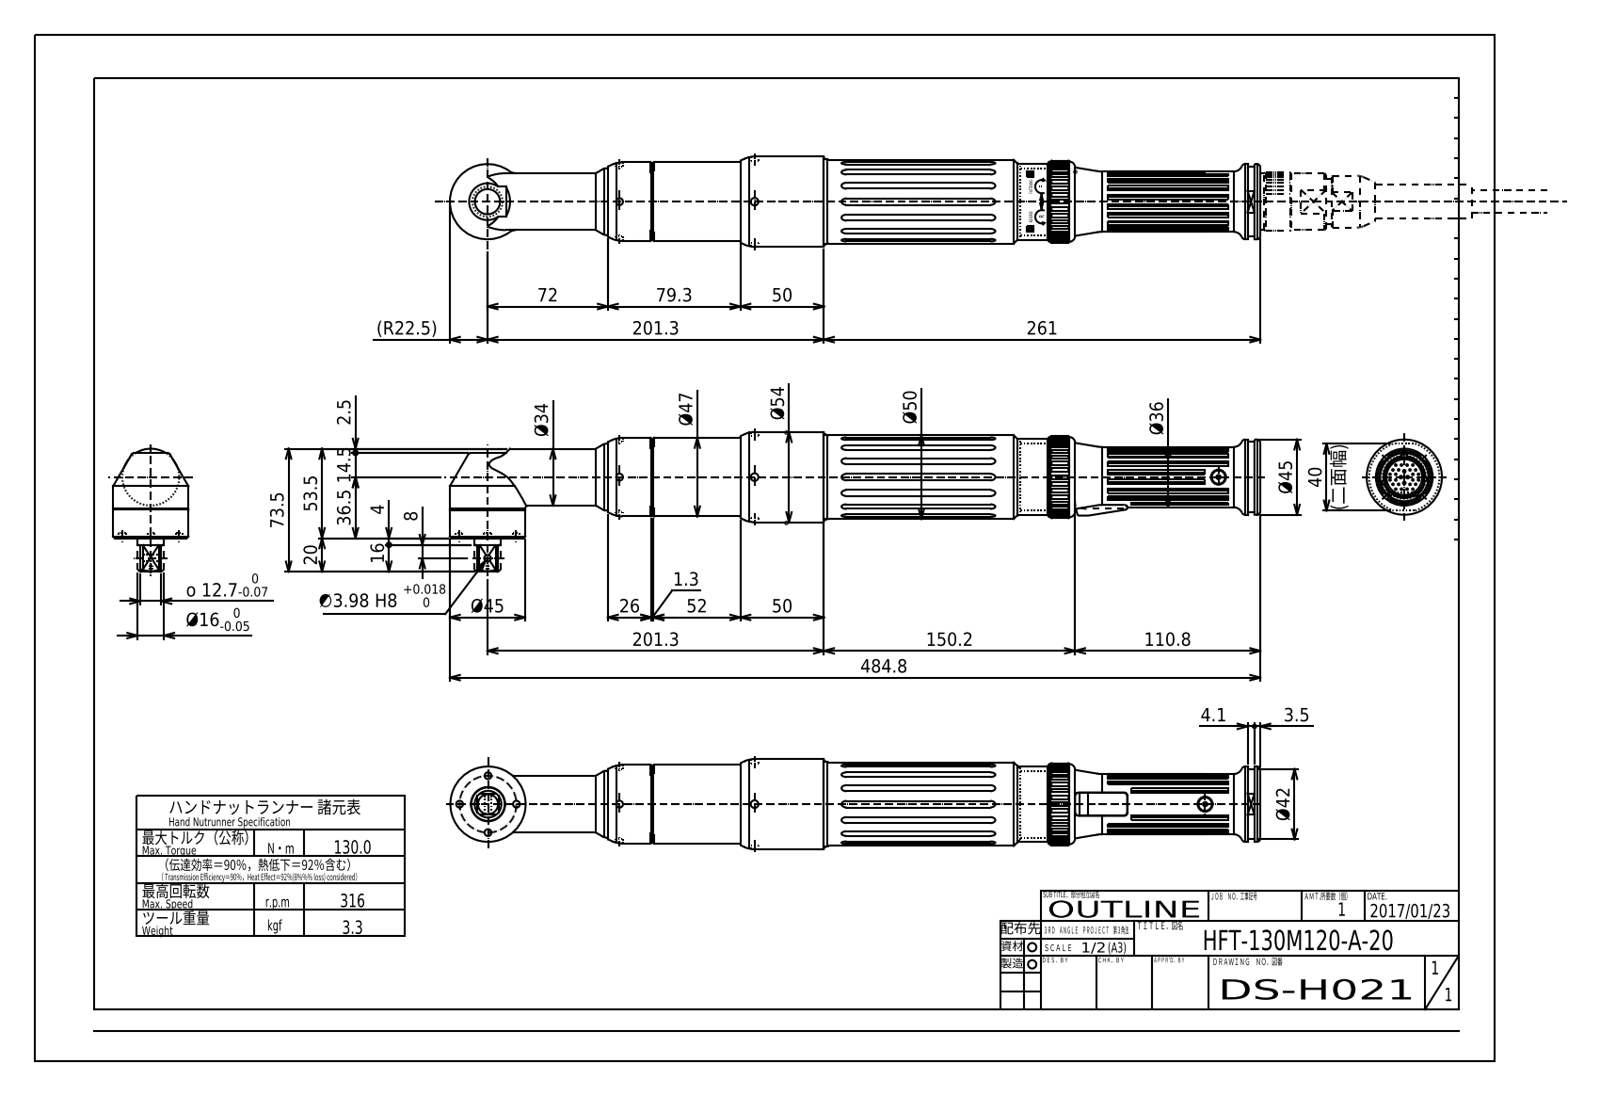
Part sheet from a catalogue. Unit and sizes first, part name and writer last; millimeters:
Units: millimetres
Overall size (bounding box): 484.75 × 83.5 × 54
Round holes (diameter × count): ⌀4.1 ×4, ⌀4.6 ×4, ⌀9 ×2, ⌀1.6 ×1, ⌀3 ×1, ⌀3.98 ×1, ⌀4.5 ×1, ⌀6 ×1, ⌀6.8 ×1, ⌀15 ×1, ⌀20.5 ×1, ⌀22.6 ×1
Round bosses / shafts (diameter × count): ⌀1 ×24, ⌀1.6 ×4, ⌀45 ×2, ⌀8 ×2, ⌀54 ×1, ⌀52 ×1, ⌀50 ×1, ⌀48 ×1
Partial cylindrical surfaces — rounded edges, fillets, slot ends (radius × count): R0.1 ×36, R1.5 ×36, R0.33 ×18, R3 ×18, R0.3 ×6, R1 ×6, R2.5 ×6, R0.88 ×2
Main face-to-face distances: 34.96, 1, 0.5, 15.6, 12.1, 3.5, 1.5, 3, 12.7, 11.13
Hole centre spacings: 17, 24.04, 34, 80.75, 80.81, 160.65, 360.05, 371.04
Volume: 763 308 mm³ · Surface area: 89 402 mm²
Bodies: 1 solid, 875 faces (464 planar, 278 cylindrical, 133 other)
Part name (STEP PRODUCT): HFT-130M120-A-20(DS-H021)_OUTLINE
STEP written by: Autodesk Inventor 2017 (AUTOMOTIVE_DESIGN)
